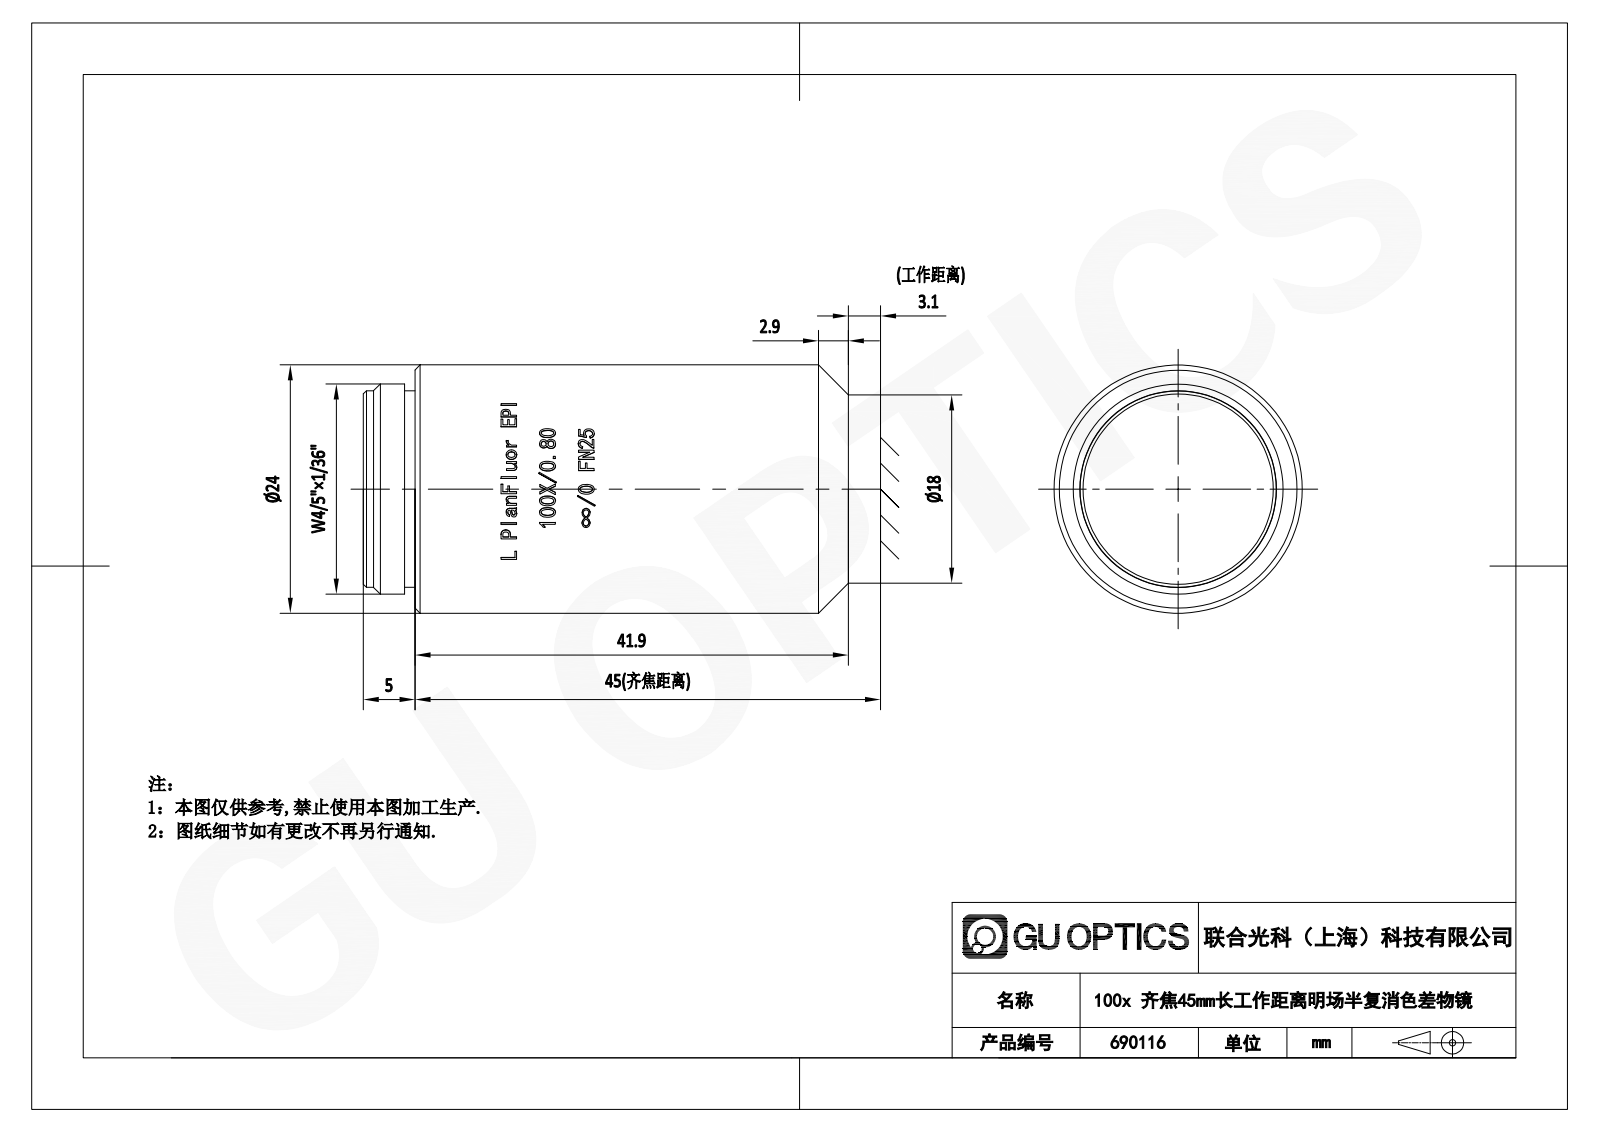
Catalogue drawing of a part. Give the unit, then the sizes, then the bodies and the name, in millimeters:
Units: millimetres
Overall size (bounding box): 46.9 × 24.05 × 24
Round bosses / shafts (diameter × count): ⌀24 ×1, ⌀20.32 ×1, ⌀19 ×1
Partial cylindrical surfaces — rounded edges, fillets, slot ends (radius × count): R12.05 ×1
Main face-to-face distances: 46.9, 5, 41.9, 1, 4, 42.9, 3, 45.9, 1.5, 14.82
Volume: 20 178 mm³ · Surface area: 4 267 mm²
Bodies: 1 solid, 309 faces (131 planar, 50 cylindrical, 128 other)
Part name (STEP PRODUCT): 690116
STEP written by: SolidWorks 2020 (CONFIG_CONTROL_DESIGN)
